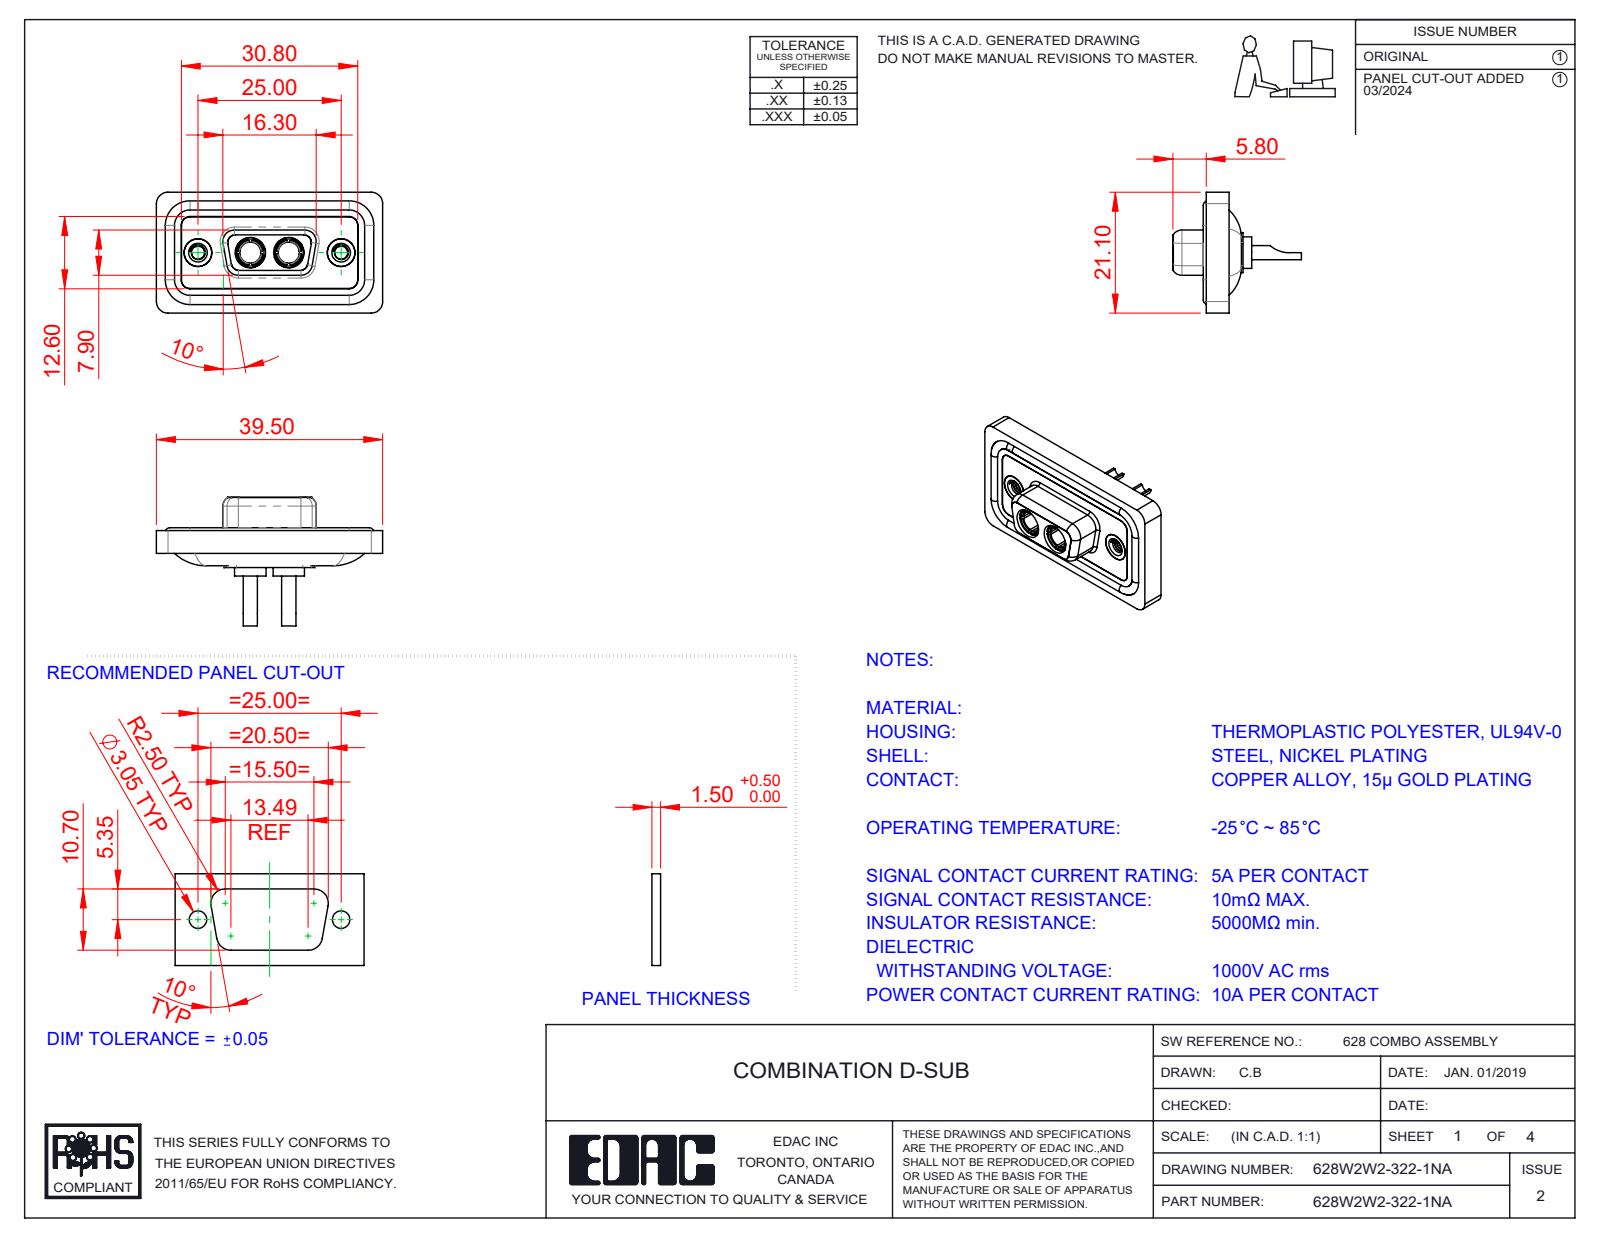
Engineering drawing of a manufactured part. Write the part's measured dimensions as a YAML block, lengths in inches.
part_name: "628W2W2-322-1NA; Power Socket_10A SC; 628Combo Shell Front_09 Contacts; 628Combo Housing_2W2 (+3 more)"
step_written_by: "SolidWorks 2023 (CONFIG_CONTROL_DESIGN)"
units: inches
bodies: {solids: 11, faces: 542, planar: 167, cylindrical: 242, other: 133}
overall_size: [1.555, 0.884, 0.831]
volume: 0.287
surface_area: 11.98
round_holes:
  - {diameter: 0.191, count: 4}
  - {diameter: 0.067, count: 2}
  - {diameter: 0.089, count: 2}
  - {diameter: 0.146, count: 2}
  - {diameter: 0.157, count: 2}
  - {diameter: 0.159, count: 2}
  - {diameter: 0.197, count: 2}
  - {diameter: 0.209, count: 2}
round_bosses_or_shafts:
  - {diameter: 0.063, count: 4}
  - {diameter: 0.217, count: 2}
  - {diameter: 0.205, count: 2}
  - {diameter: 0.195, count: 2}
  - {diameter: 0.195, count: 2}
  - {diameter: 0.189, count: 2}
  - {diameter: 0.187, count: 2}
  - {diameter: 0.148, count: 2}
partial_cylinders:
  - {radius: 0.059, count: 22}
  - {radius: 0.079, count: 18}
  - {radius: 0.053, count: 8}
  - {radius: 0.063, count: 8}
  - {radius: 0.01, count: 4}
  - {radius: 0.02, count: 4}
  - {radius: 0.024, count: 4}
  - {radius: 0.026, count: 4}
face_to_face_distances: [0.016, 0.071, 0.043, 0.114, 0.02, 0.063, 0.222, 0.293, 0.059, 0.211]
hole_center_spacings: [0.36, 0.624, 0.265, 0.984]
